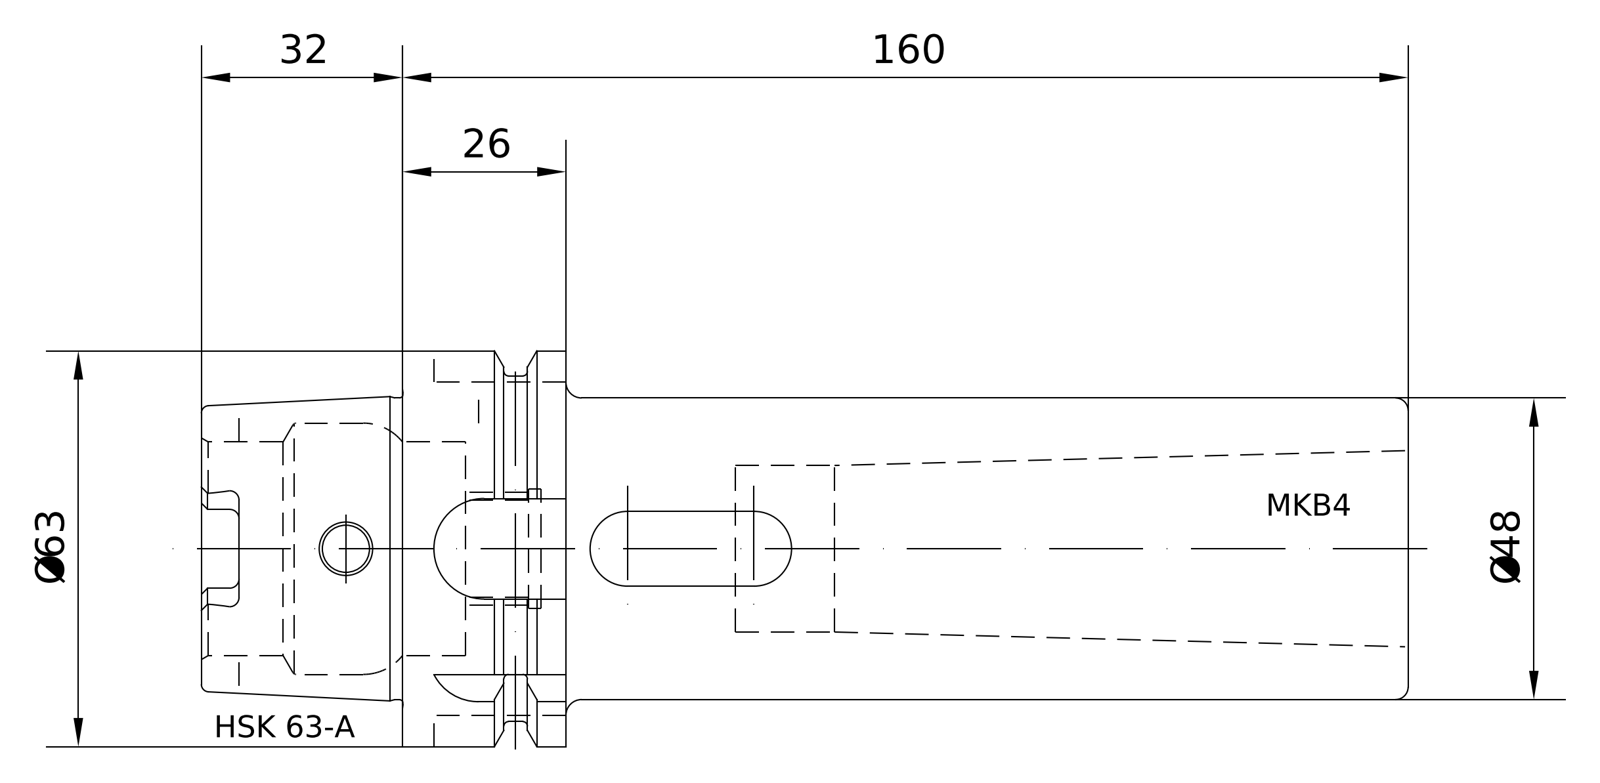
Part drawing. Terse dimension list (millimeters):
name: A63-080-04
written by: PRO/ENGINEER BY PARAMETRIC TECHNOLOGY CORPORATION, 2010430 (CONFIG_CONTROL_DESIGN)
unit: mm
bodies: 1 solid, 174 faces (58 planar, 48 cylindrical, 68 other)
size: 192 × 63 × 63
volume: 255 605 mm³; area: 51 871 mm²
holes: 1× ⌀7.5, 1× ⌀10, 1× ⌀16.92, 1× ⌀18.32, 1× ⌀18.66, 1× ⌀26.5, 1× ⌀34, 1× ⌀40
bosses: 1× ⌀63, 1× ⌀55, 1× ⌀48.04, 1× ⌀48, 1× ⌀18
rounds: 6× R1.5, 4× R3, 1× R8, 1× R8.02, 1× R9.02
face distances: 26, 160, 134, 10, 53, 27, 107, 16, 43, 150
